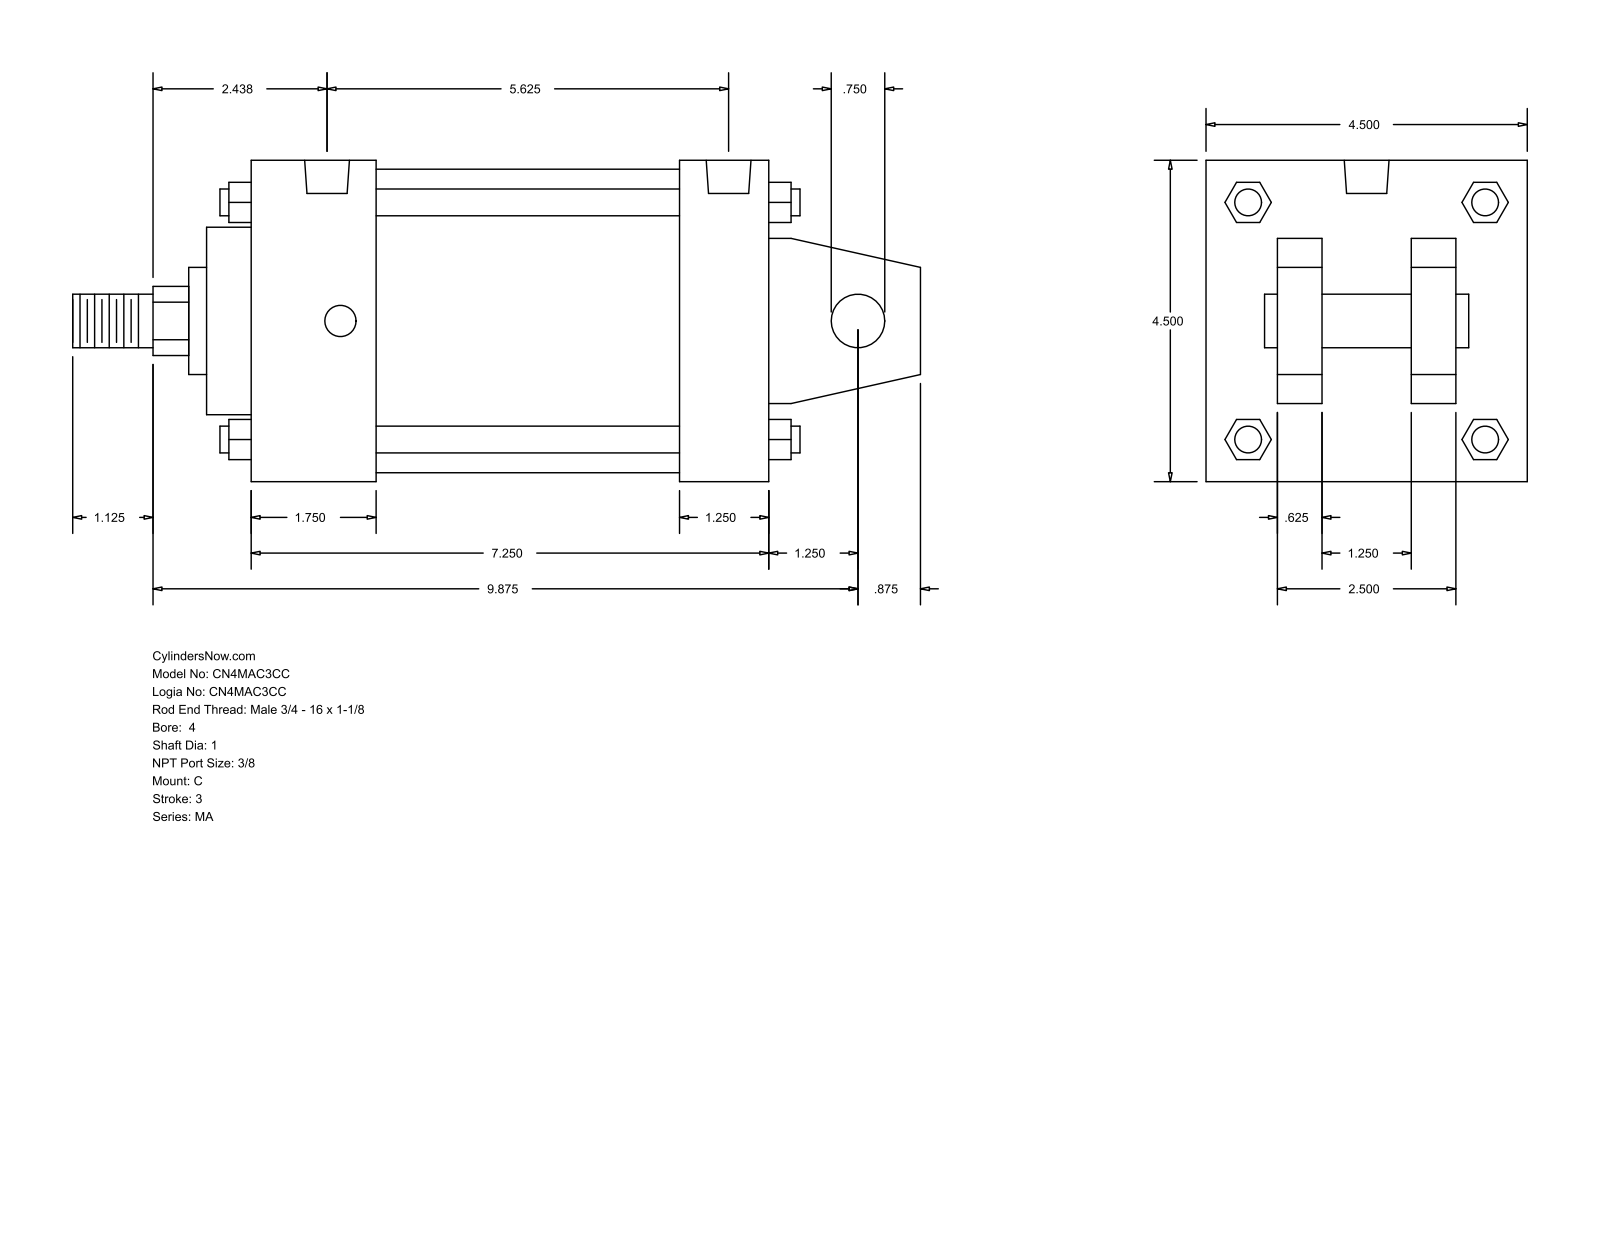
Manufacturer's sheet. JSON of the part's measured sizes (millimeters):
{"part_name": "MA_C__0400_1", "step_written_by": "GSSL Pune (CONFIG_CONTROL_DESIGN)", "units": "millimeters", "bodies": {"solids": 0, "faces": 141, "planar": 109, "cylindrical": 32, "other": 0}, "overall_size": [301.62, 114.3, 114.3], "round_holes": [[11.11, 4], [15.93, 2]], "round_bosses_or_shafts": [[9.53, 4], [19.05, 2], [107.95, 1], [66.67, 1], [38.1, 1], [25.4, 1]], "partial_cylinders_radius": [[12.29, 1]], "face_to_face_distances": [114.3, 184.15, 15.87, 73.03, 41.27, 25.4, 88.9, 47.63, 152.4, 31.75], "hole_center_spacings": [4.76, 133.36, 138.12, 142.88]}
